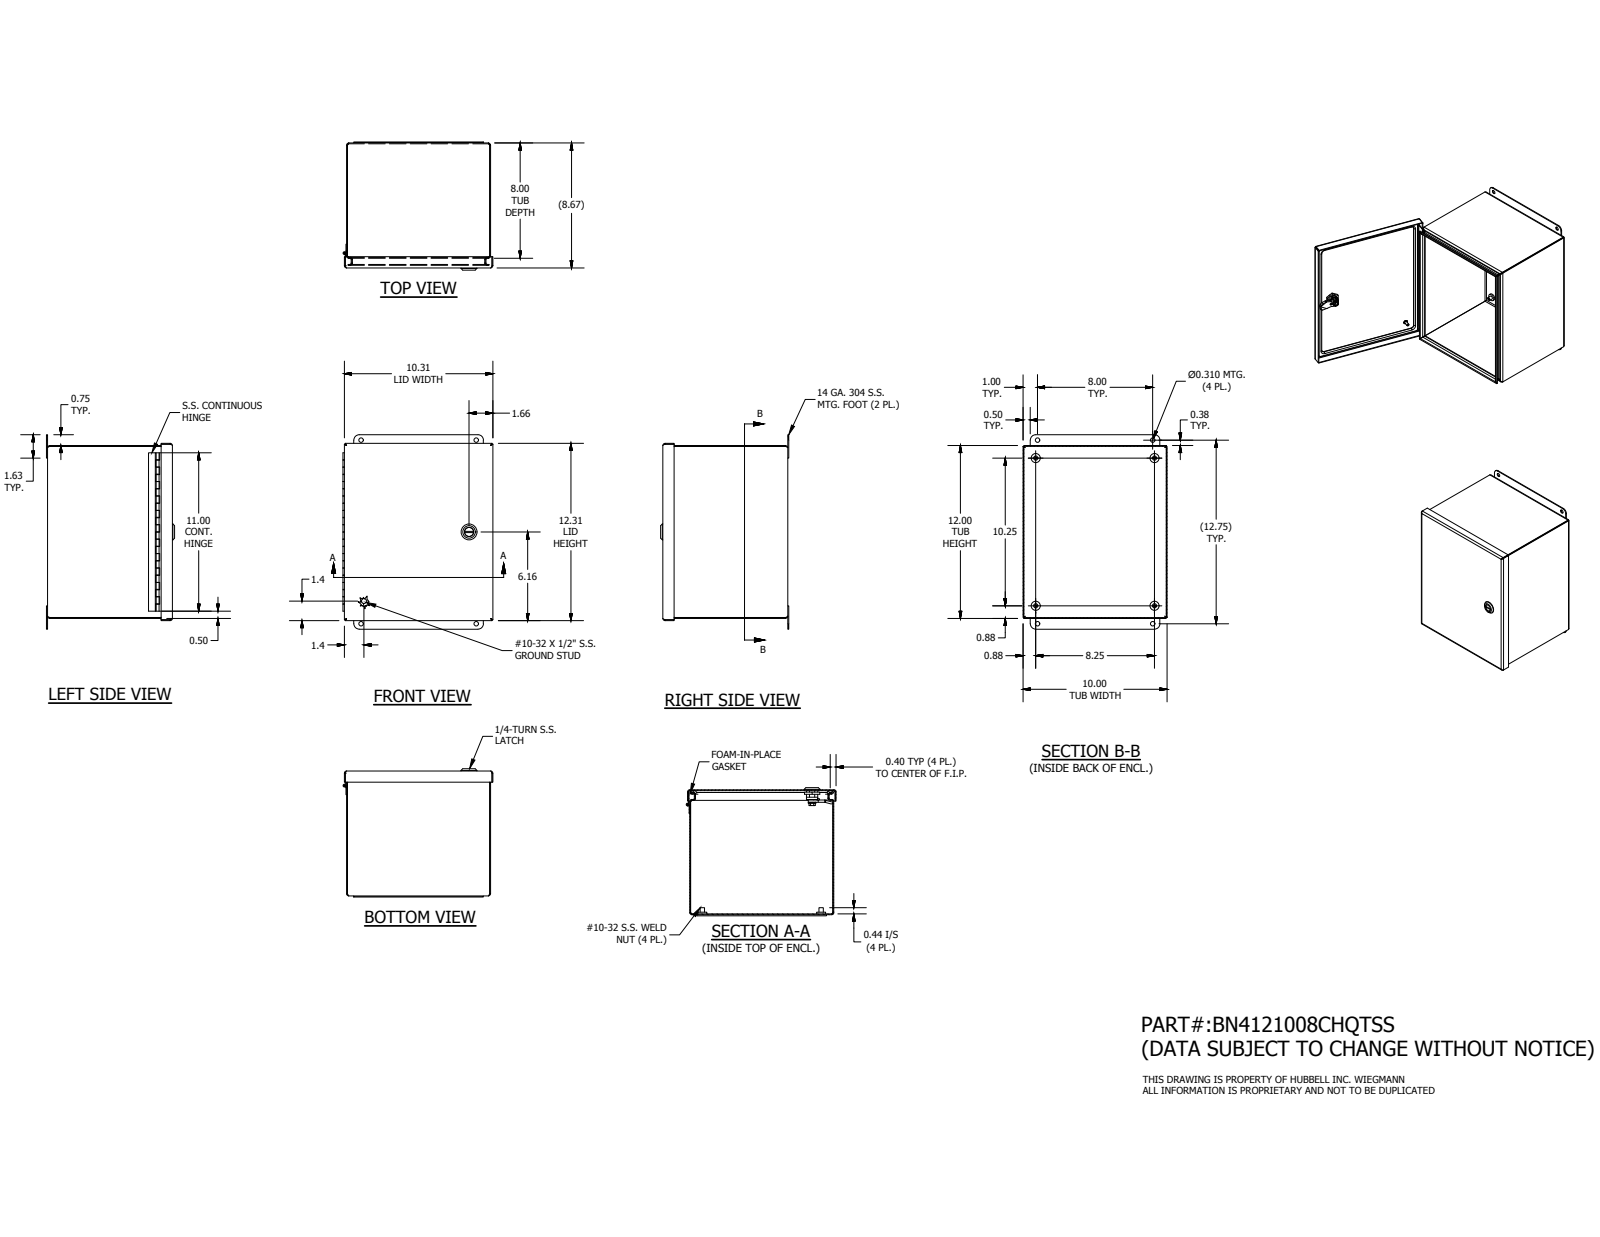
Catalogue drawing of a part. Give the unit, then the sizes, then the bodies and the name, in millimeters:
Units: millimetres
Overall size (bounding box): 342.9 × 264.46 × 226.19
Round holes (diameter × count): ⌀3.96 ×4, ⌀7.87 ×4, ⌀2.96 ×1, ⌀5 ×1, ⌀8 ×1, ⌀10 ×1, ⌀10.2 ×1, ⌀16.1 ×1
Round bosses / shafts (diameter × count): ⌀15.88 ×4, ⌀7.62 ×4, ⌀28 ×1, ⌀19.8 ×1, ⌀16 ×1, ⌀15.2 ×1, ⌀13.5 ×1, ⌀12.8 ×1
Partial cylindrical surfaces — rounded edges, fillets, slot ends (radius × count): R2.38 ×20, R3.88 ×20, R3.17 ×16, R0.5 ×8, R4 ×4, R9.53 ×4, R2.31 ×2, R6.45 ×1
Main face-to-face distances: 1.5, 1.49, 303.3, 218.79, 220.28, 217.29, 218.78, 252.51, 254, 251.01
Hole centre spacings: 31.91, 292.12, 357.65, 131.14, 203.2, 208.8, 208.81, 209.55
Volume: 761 548 mm³ · Surface area: 962 760 mm²
Bodies: 19 solids, 628 faces (335 planar, 199 cylindrical, 94 other)
Part name (STEP PRODUCT): BN41210CHQTSSLID; 12x10; 34855; H4050551LH (+8 more)
STEP written by: Autodesk Inventor 2016 (AUTOMOTIVE_DESIGN)
